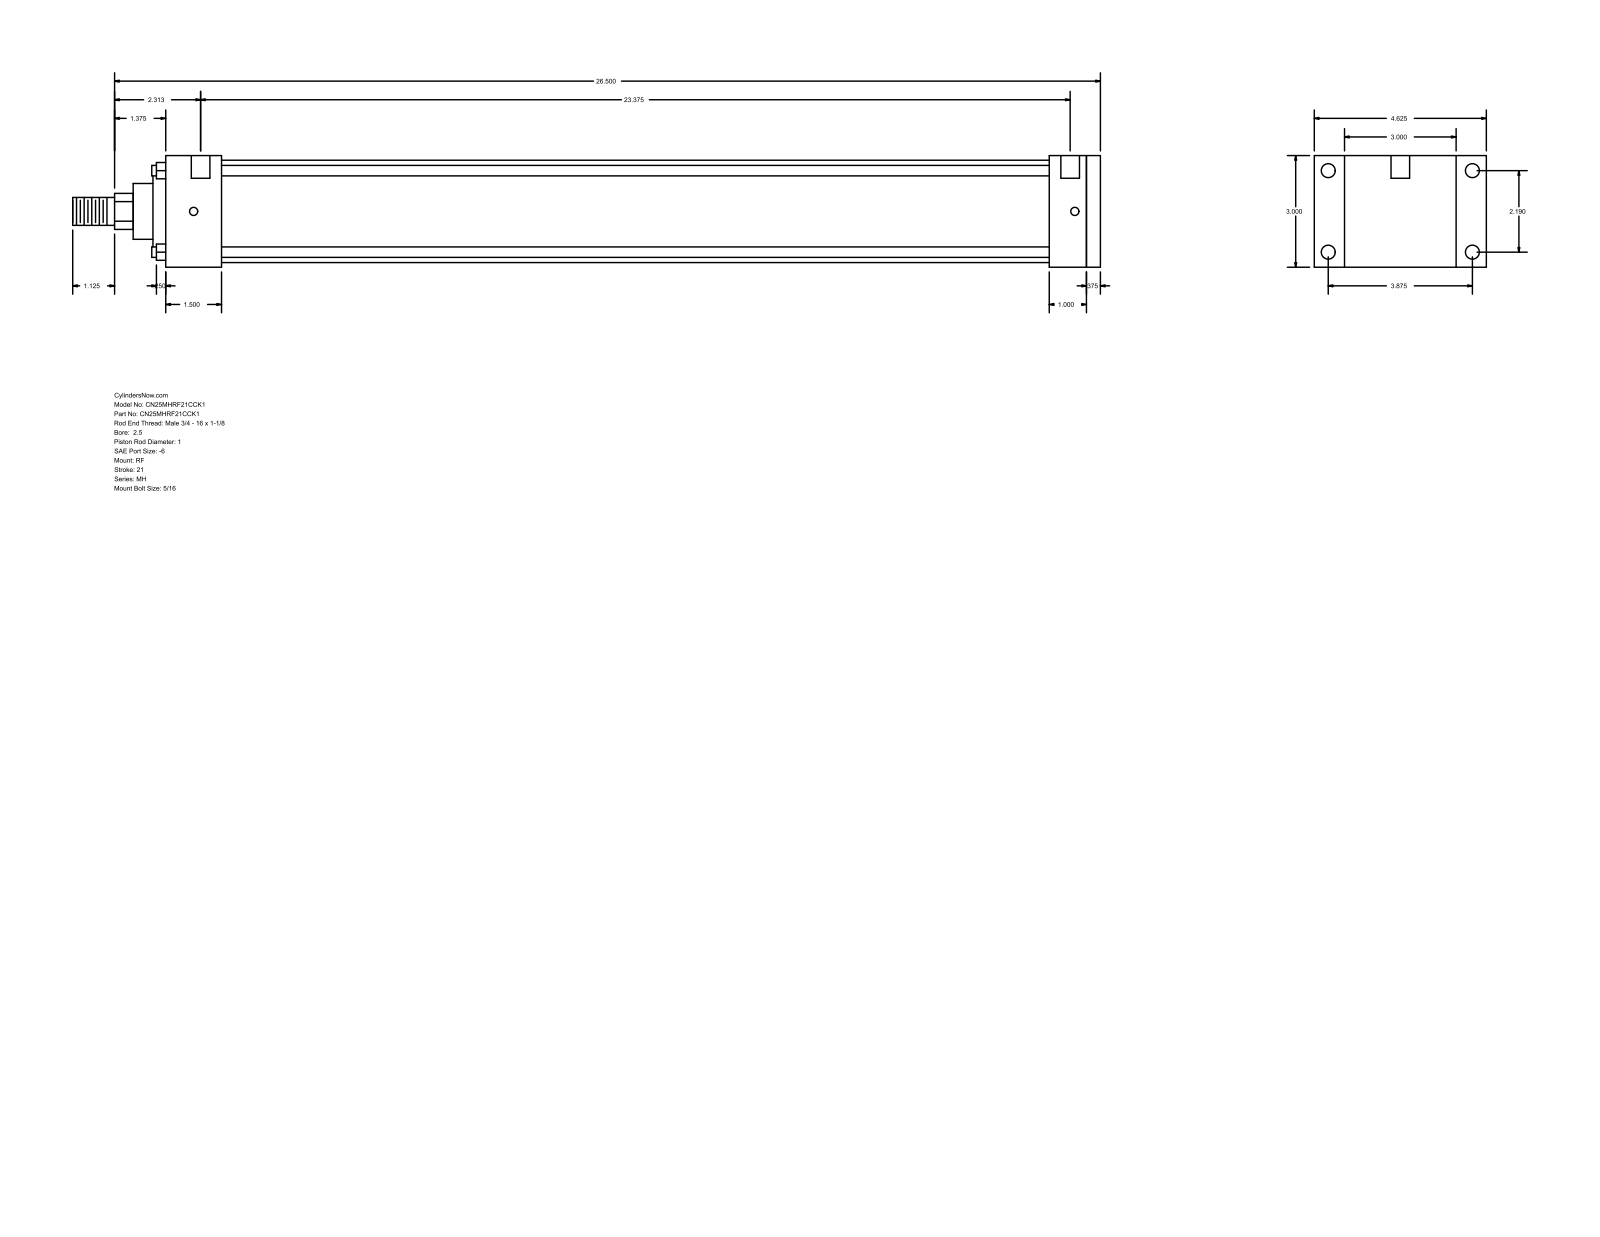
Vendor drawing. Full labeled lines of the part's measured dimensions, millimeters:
Part name (STEP PRODUCT): MH_RF__0250_1
STEP written by: GSSL Pune (CONFIG_CONTROL_DESIGN)
Units: millimetres
Bodies: 0 solids, 94 faces (65 planar, 29 cylindrical, 0 other)
Overall size (bounding box): 701.67 × 117.47 × 76.2
Round holes (diameter × count): ⌀5.56 ×4, ⌀9.53 ×4, ⌀12.7 ×2
Round bosses / shafts (diameter × count): ⌀7.14 ×4, ⌀69.85 ×1, ⌀60.33 ×1, ⌀38.1 ×1, ⌀25.4 ×1, ⌀19.05 ×1
Partial cylindrical surfaces — rounded edges, fillets, slot ends (radius × count): R12.29 ×1
Main face-to-face distances: 76.2, 9.52, 638.18, 628.66, 603.25, 25.41, 34.93, 38.11, 565.14, 590.55
Hole centre spacings: 55.62, 98.42, 113.05, 601.66, 3.18, 4.76, 593.72, 596.9
